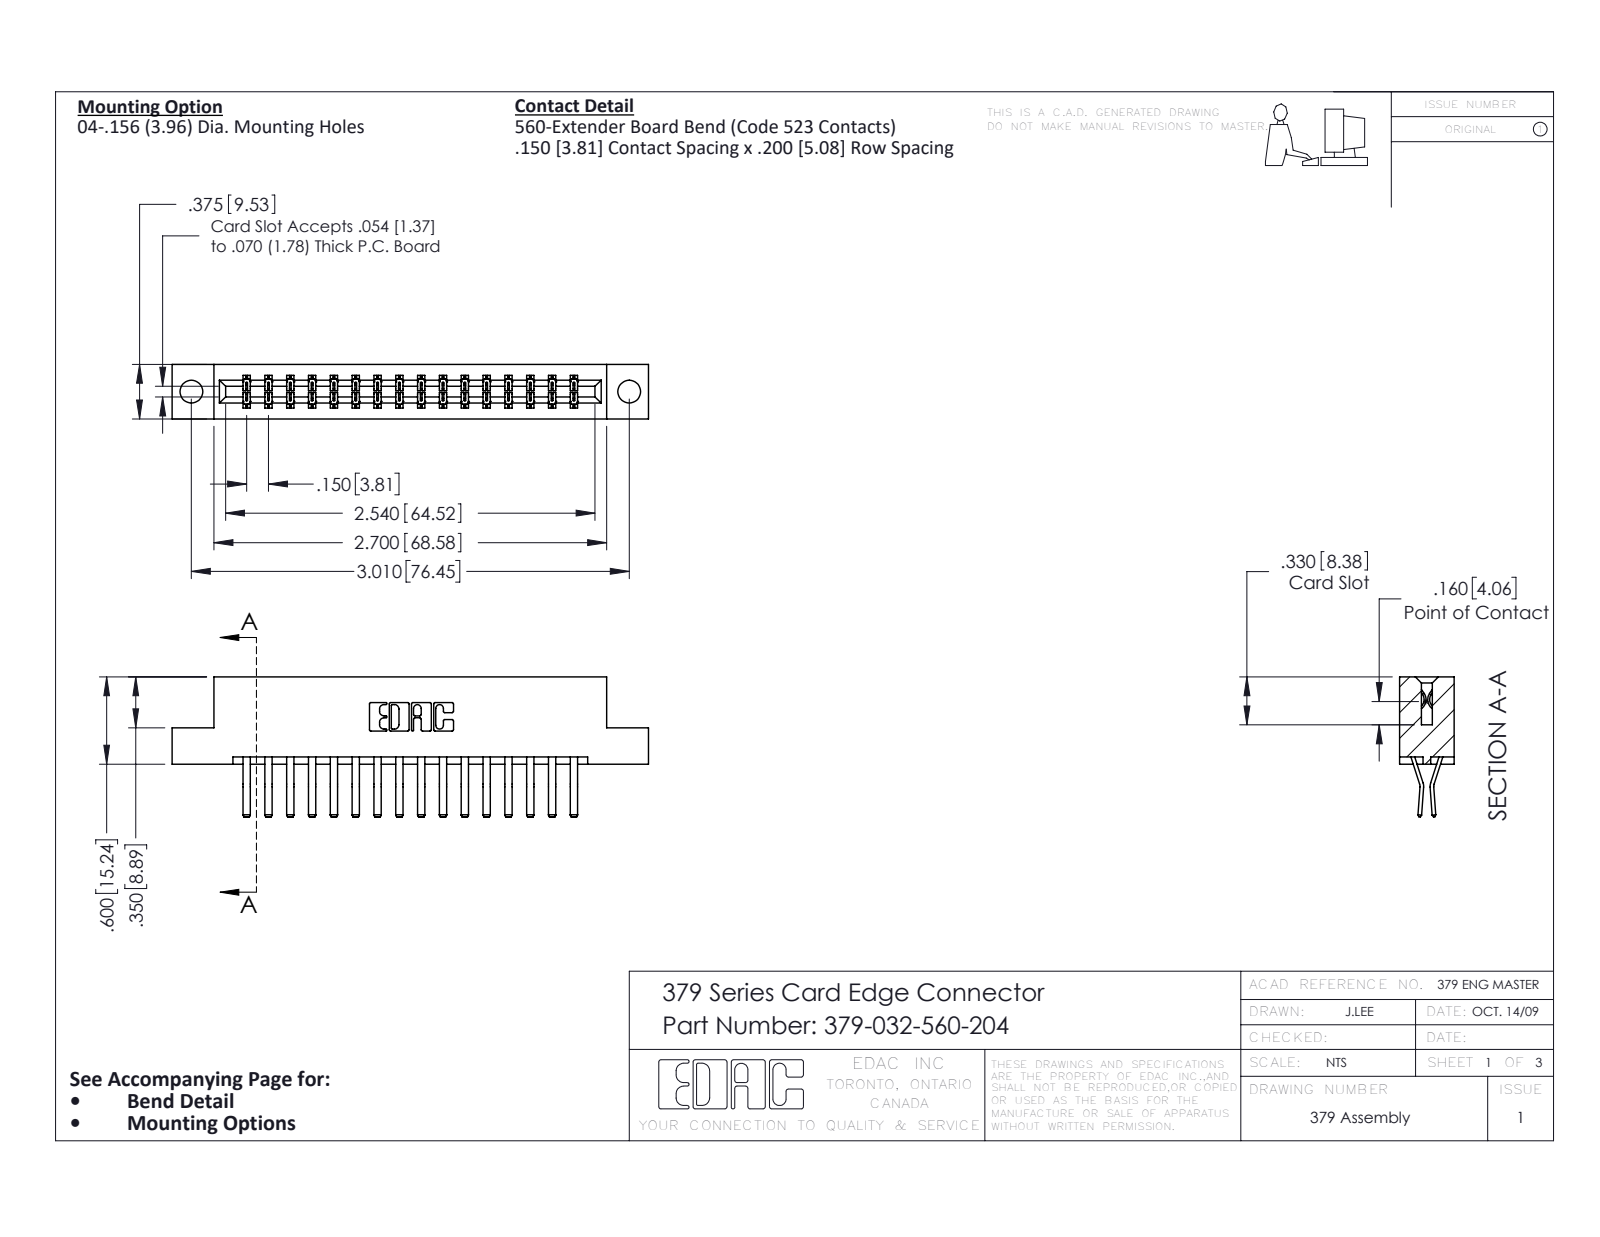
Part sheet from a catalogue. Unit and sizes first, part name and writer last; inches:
Units: inches
Overall size (bounding box): 3.275 × 0.962 × 0.375
Round holes (diameter × count): ⌀0.156 ×2
Partial cylindrical surfaces — rounded edges, fillets, slot ends (radius × count): R0.006 ×48, R0.01 ×22, R0.007 ×6, R0.031 ×6, R0.026 ×3, R0.01 ×2, R0.014 ×2, R0.022 ×2
Main face-to-face distances: 0.3, 0.075, 0.6, 0.375, 0.15, 0.45, 0.2, 0.225, 0.75, 0.9
Hole centre spacings: 3.01
Volume: 0.528 in³ · Surface area: 15.33 in²
Bodies: 33 solids, 1842 faces (1222 planar, 620 cylindrical, 0 other)
Part name (STEP PRODUCT): 345-292-001_560 Tail; 379-032-560-204; 379 Part_Flush - .156 Dia - TH
STEP written by: SolidWorks 2020 (CONFIG_CONTROL_DESIGN)
